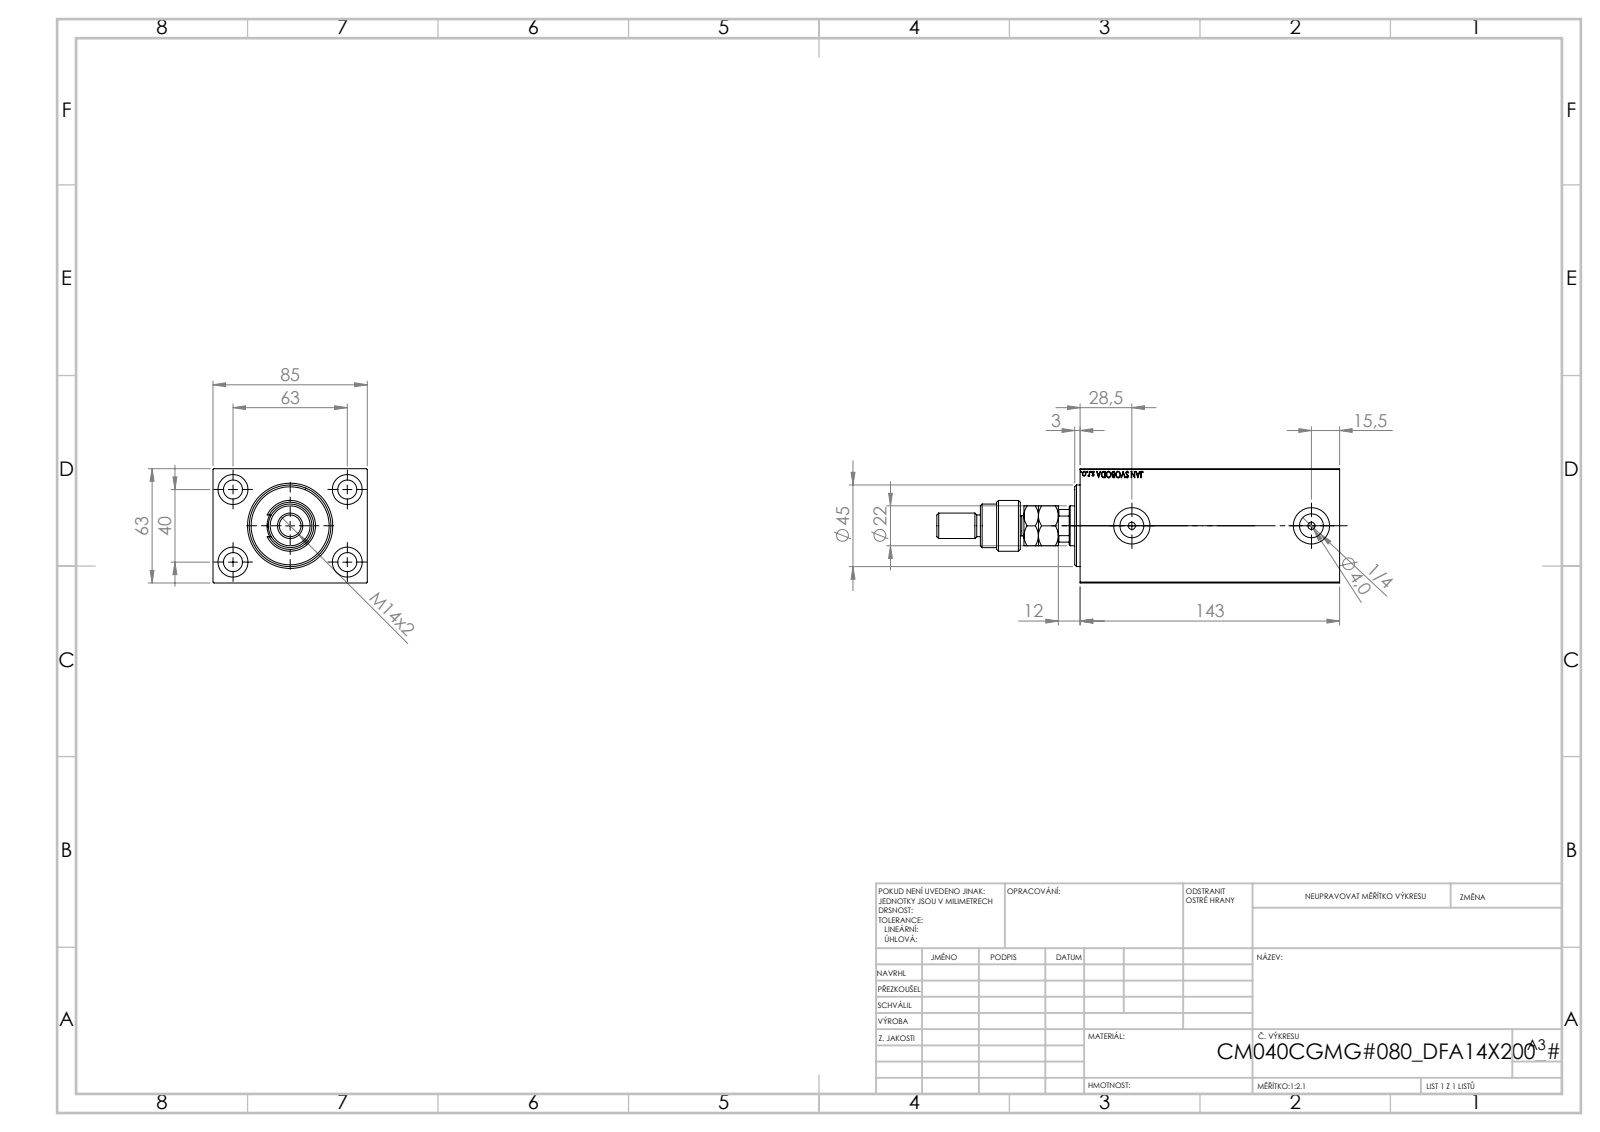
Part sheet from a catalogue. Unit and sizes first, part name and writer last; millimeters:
Units: millimetres
Overall size (bounding box): 222 × 85 × 63
Round holes (diameter × count): ⌀10.5 ×4, ⌀16.5 ×4, ⌀4 ×2, ⌀13.16 ×2, ⌀20 ×2, ⌀12.5 ×1, ⌀22 ×1, ⌀25.5 ×1, ⌀40 ×1, ⌀42 ×1, ⌀45 ×1
Round bosses / shafts (diameter × count): ⌀28 ×1, ⌀24 ×1, ⌀18 ×1, ⌀14 ×1, ⌀12 ×1, ⌀11 ×1
Partial cylindrical surfaces — rounded edges, fillets, slot ends (radius × count): R9.75 ×1, R10.5 ×1
Main face-to-face distances: 63, 85, 12, 131, 143, 15, 119, 51, 3, 1
Hole centre spacings: 37.31, 40, 63, 74.63, 99
Volume: 657 756 mm³ · Surface area: 119 353 mm²
Bodies: 5 solids, 947 faces (436 planar, 73 cylindrical, 438 other)
Part name (STEP PRODUCT): FEMALE_PART_FOR_DFA; V450CM_C_VCP; V450CM_C_Body; V450CM_VC_B (+1 more)
STEP written by: SolidWorks 2019 (CONFIG_CONTROL_DESIGN)
